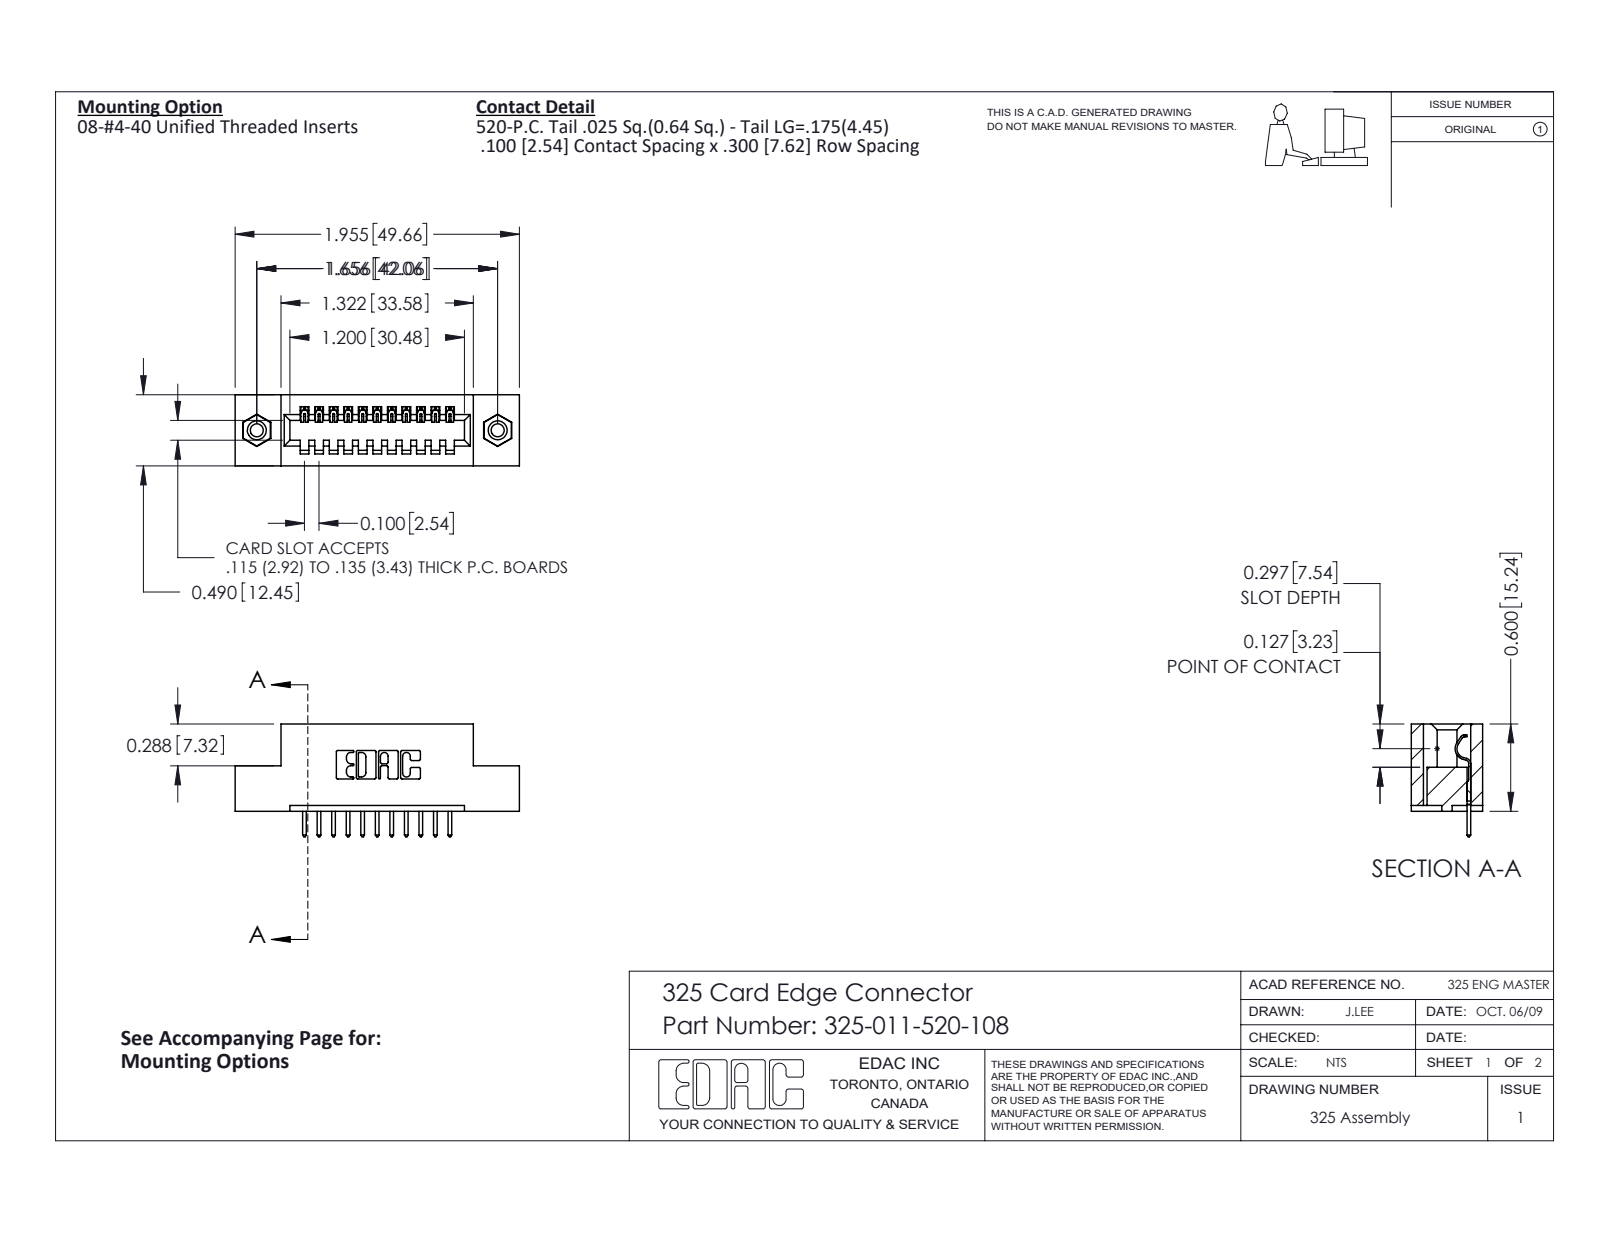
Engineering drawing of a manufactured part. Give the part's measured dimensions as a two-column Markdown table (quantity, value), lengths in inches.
| quantity | value |
| --- | --- |
| part name | 325-292-001_325-293-120; 345-250-001_345-250-003-102; 325 Part_TI; 325-011-520-108 |
| STEP written by | SolidWorks 2016 (CONFIG_CONTROL_DESIGN) |
| units | inches |
| bodies | 14 solids, 812 faces (564 planar, 232 cylindrical, 16 other) |
| overall size | 1.955 × 0.775 × 0.49 |
| volume | 0.368 in³ |
| surface area | 9.233 in² |
| round holes (diameter × count) | 0.089 × 2, 0.125 × 2, 0.16 × 2 |
| round bosses / shafts (diameter × count) | 0.155 × 2 |
| partial cylindrical surfaces (radius × count) | 0.006 × 22, 0.01 × 22, 0.01 × 22, 0.007 × 6, 0.031 × 6, 0.026 × 3, 0.014 × 1, 0.022 × 1 |
| main face-to-face distances | 0.3, 0.083, 0.407, 0.49, 0.04, 0.1, 0.2, 0.6, 0.4, 0.56 |
| hole center spacings | 1.656 |
